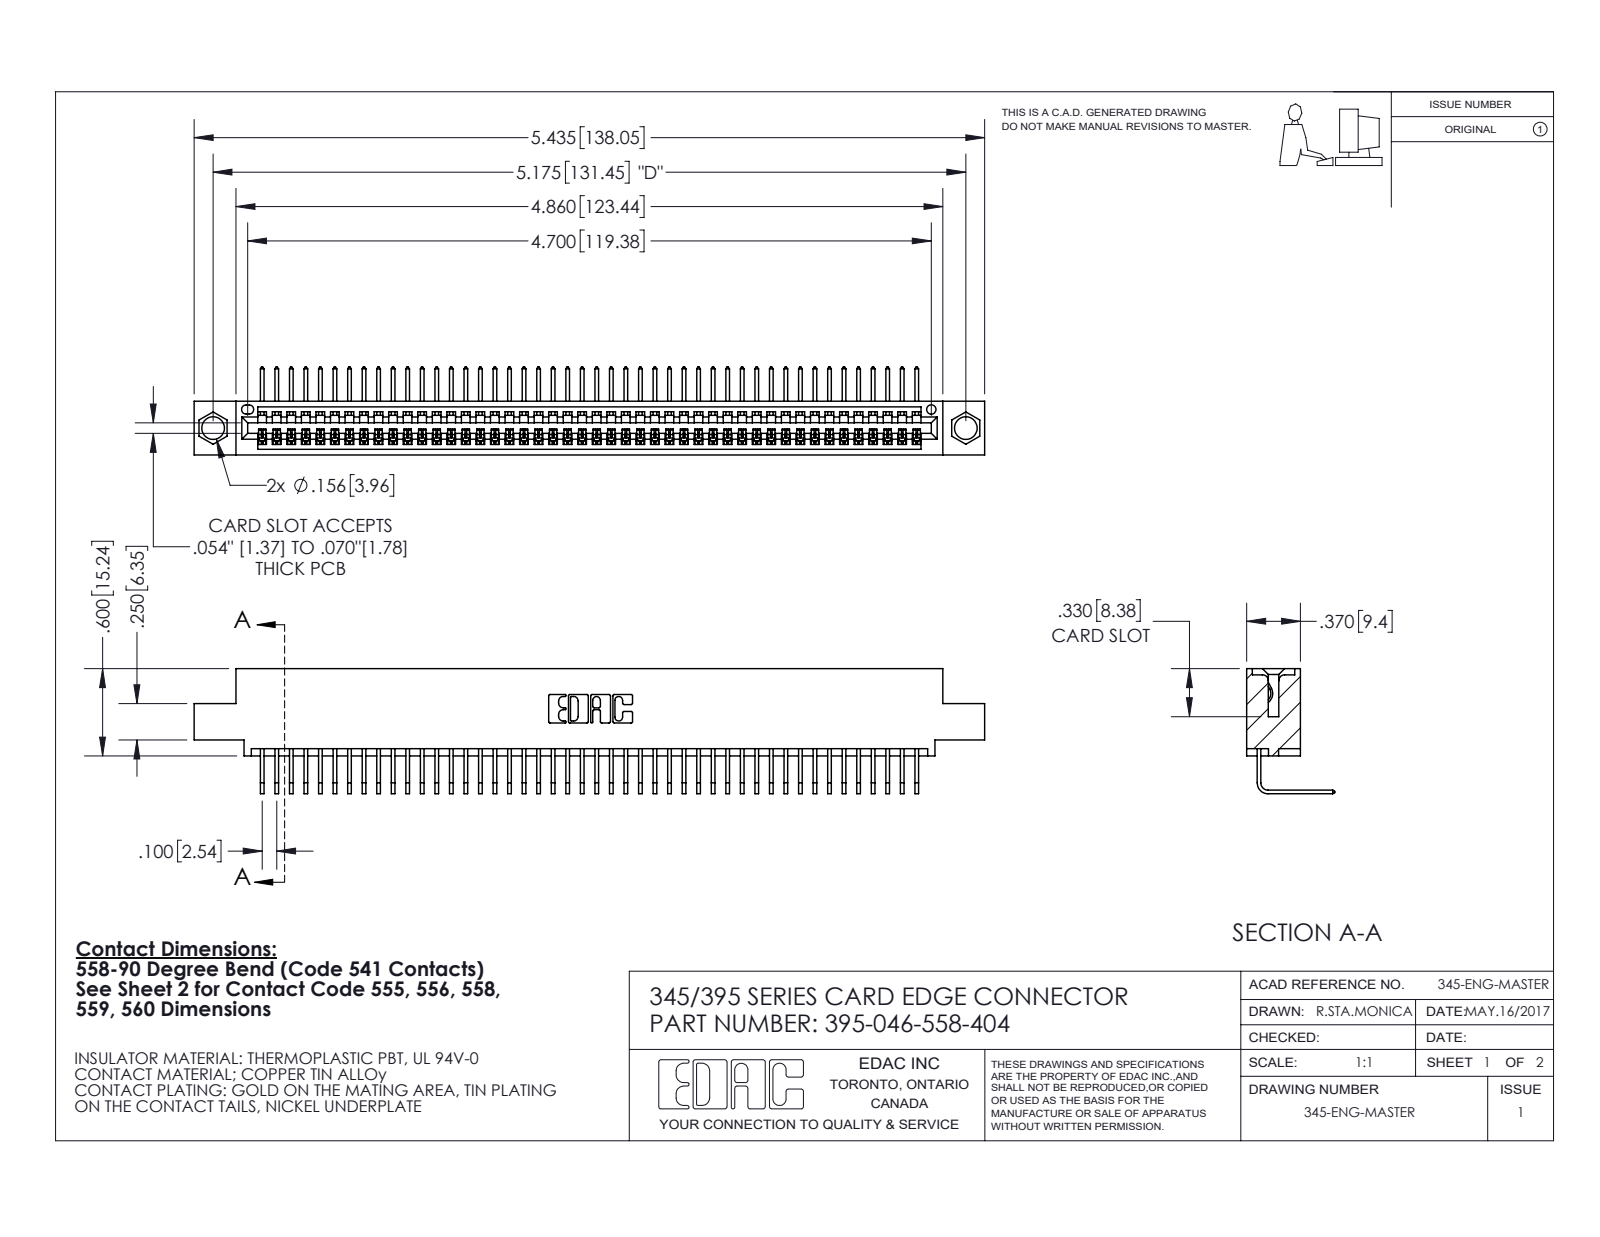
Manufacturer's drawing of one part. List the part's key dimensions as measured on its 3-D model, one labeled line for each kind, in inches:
Part name (STEP PRODUCT): 395-046-558-404; 345 Part_0.110 Offset - 0.156 Dia-TI; 345-292-001_558 Tail - 2
STEP written by: SolidWorks 2020 (CONFIG_CONTROL_DESIGN)
Units: inches
Bodies: 47 solids, 2904 faces (2030 planar, 874 cylindrical, 0 other)
Overall size (bounding box): 5.435 × 0.859 × 0.605
Volume: 0.801 in³ · Surface area: 28.39 in²
Round holes (diameter × count): ⌀0.156 ×2, ⌀0.064 ×1
Partial cylindrical surfaces — rounded edges, fillets, slot ends (radius × count): R0.006 ×92, R0.01 ×22, R0.007 ×6, R0.031 ×6, R0.026 ×3, R0.031 ×2, R0.04 ×2, R0.014 ×1
Main face-to-face distances: 0.072, 0.298, 0.37, 0.2, 0.098, 0.272, 0.025, 0.225, 0.149, 0.072
Hole centre spacings: 0.27, 4.939, 5.175
